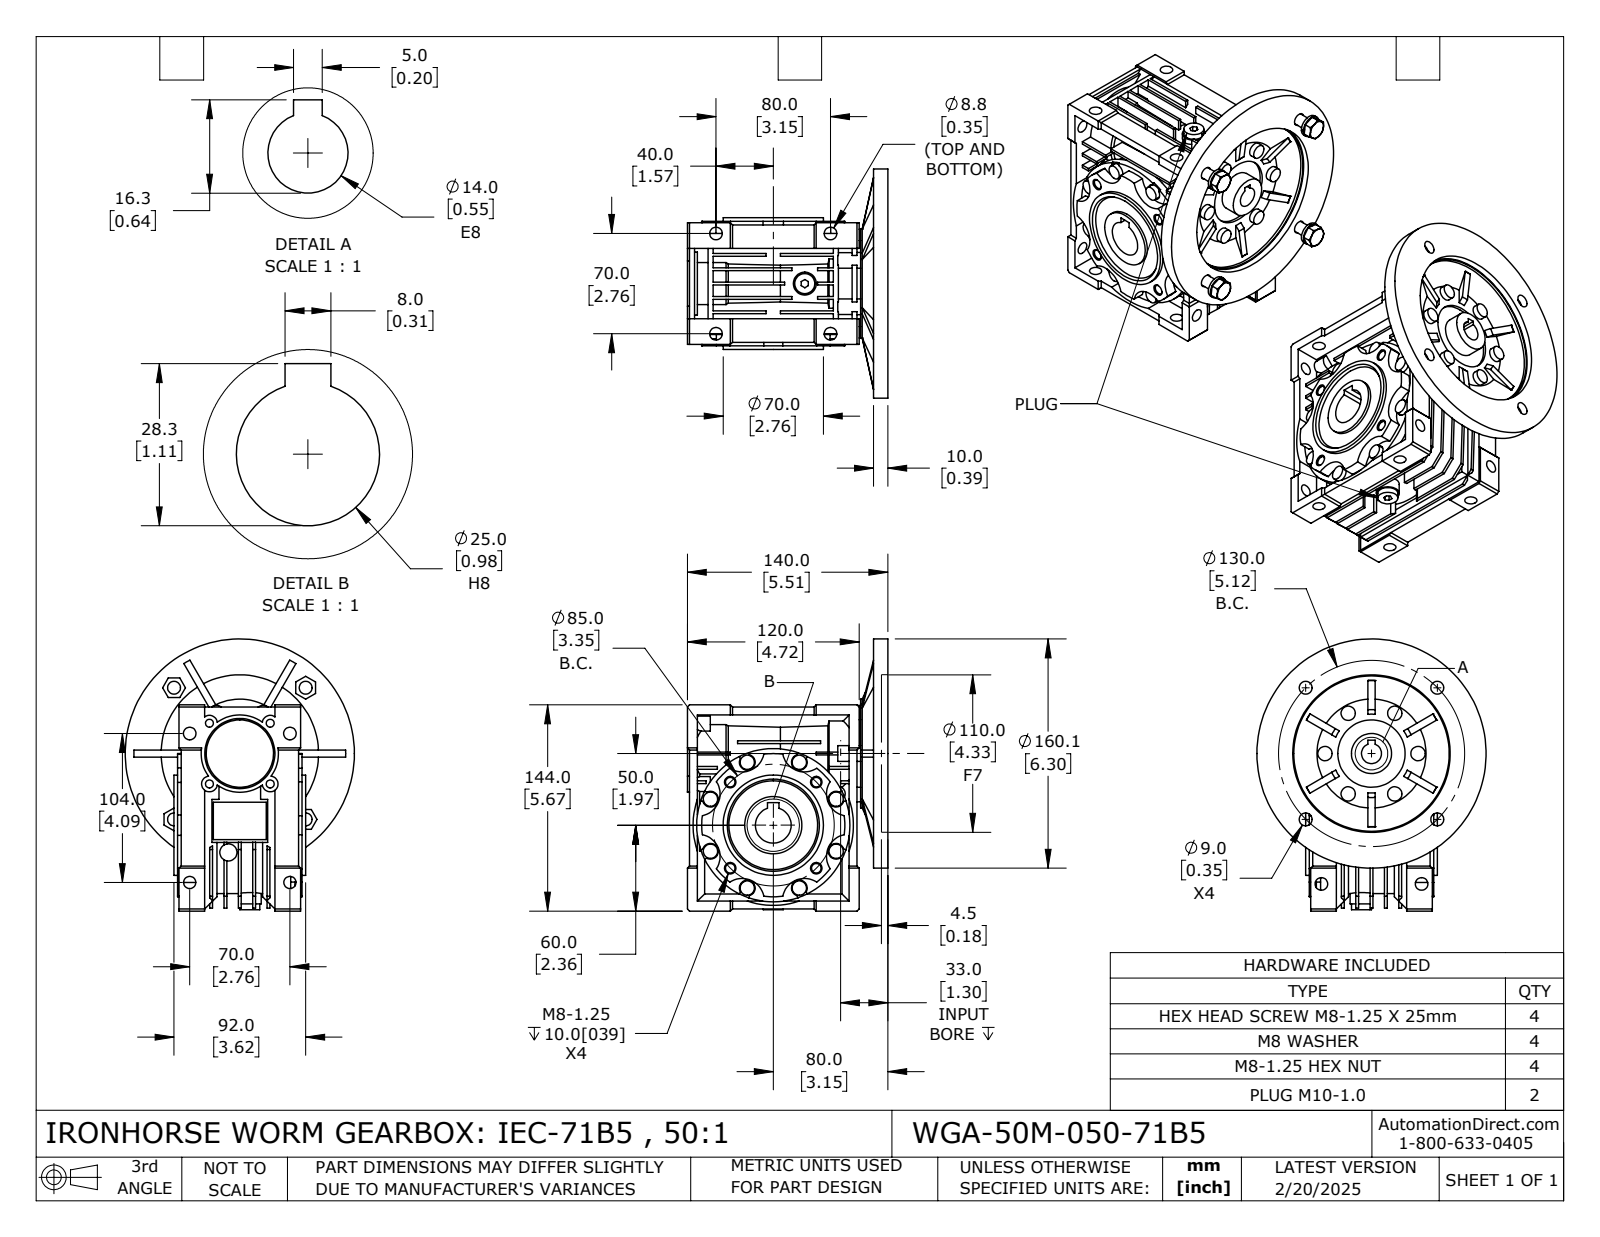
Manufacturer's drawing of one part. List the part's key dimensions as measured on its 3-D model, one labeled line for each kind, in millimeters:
Part name (STEP PRODUCT): WGA-50M-050-71B5
STEP written by: SolidWorks 2024 (CONFIG_CONTROL_DESIGN)
Units: millimetres
Bodies: 7 solids, 1007 faces (577 planar, 316 cylindrical, 114 other)
Overall size (bounding box): 190.03 × 160.06 × 140
Volume: 1 146 000 mm³ · Surface area: 256 628 mm²
Round holes (diameter × count): ⌀8.8 ×8, ⌀8.5 ×6, ⌀9 ×6, ⌀5.55 ×4, ⌀6.65 ×2, ⌀6.65 ×2, ⌀14 ×1, ⌀15 ×1, ⌀25 ×1, ⌀28 ×1, ⌀34 ×1, ⌀40 ×1
Round bosses / shafts (diameter × count): ⌀10 ×14, ⌀16 ×2, ⌀14 ×2, ⌀9.8 ×2, ⌀8.3 ×2, ⌀160.06 ×1, ⌀107 ×1, ⌀76 ×1
Partial cylindrical surfaces — rounded edges, fillets, slot ends (radius × count): R5.5 ×18, R6 ×8, R15 ×8, R15.5 ×8, R20.76 ×1, R46 ×1, R47.7 ×1, R50 ×1
Main face-to-face distances: 10, 2, 7, 5.5, 8, 1.5, 20, 5, 55, 35
Hole centre spacings: 71.58, 70, 30, 35, 42.42, 42.5, 60.1, 65
